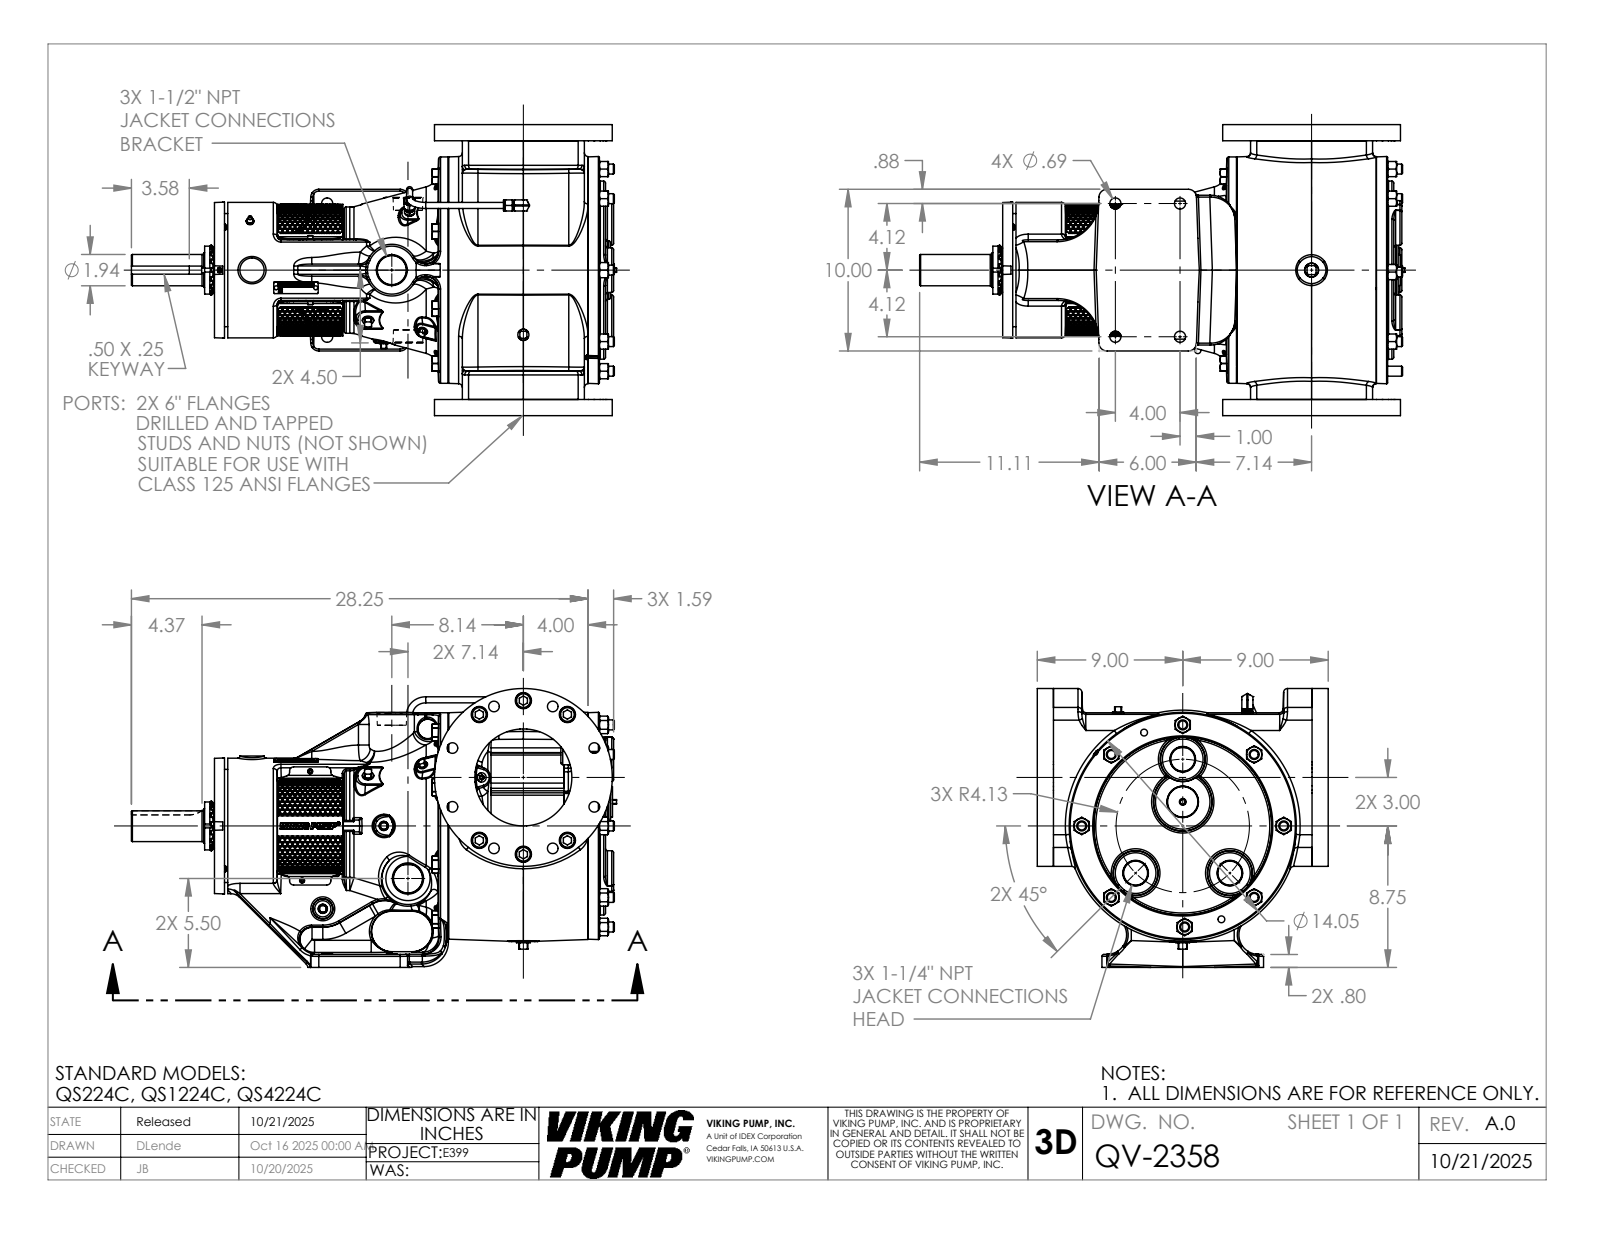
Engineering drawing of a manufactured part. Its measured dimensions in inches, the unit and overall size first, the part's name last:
Units: inches
Overall size (bounding box): 30.014 × 18 × 17.25
Round holes (diameter × count): ⌀0.25 ×9, ⌀0.266 ×8, ⌀0.656 ×8, ⌀1.157 ×8, ⌀1 ×6, ⌀0.688 ×4, ⌀0.875 ×4, ⌀0.159 ×2, ⌀0.313 ×2, ⌀0.422 ×2, ⌀0.453 ×1, ⌀2.157 ×1
Round bosses / shafts (diameter × count): ⌀0.617 ×8, ⌀0.937 ×6, ⌀0.375 ×5, ⌀0.312 ×3, ⌀0.19 ×3, ⌀0.687 ×2, ⌀0.563 ×2, ⌀0.498 ×2
Partial cylindrical surfaces — rounded edges, fillets, slot ends (radius × count): R0.12 ×54, R0.75 ×22, R0.015 ×18, R0.092 ×18, R0.07 ×16, R0.5 ×12, R0.25 ×10, R1 ×10
Main face-to-face distances: 18, 0.38, 1, 17, 23.817, 24.197, 3.82, 19.998, 20.378, 0.843
Hole centre spacings: 3.75, 2.079, 4.75, 5.783, 2.713, 3.133, 3.788, 5.423
Volume: 2 889 in³ · Surface area: 2 300 in²
Bodies: 1 solid, 4035 faces (1342 planar, 658 cylindrical, 2035 other)
Part name (STEP PRODUCT): QV-2358
STEP written by: SolidWorks 2024 (AUTOMOTIVE_DESIGN)
